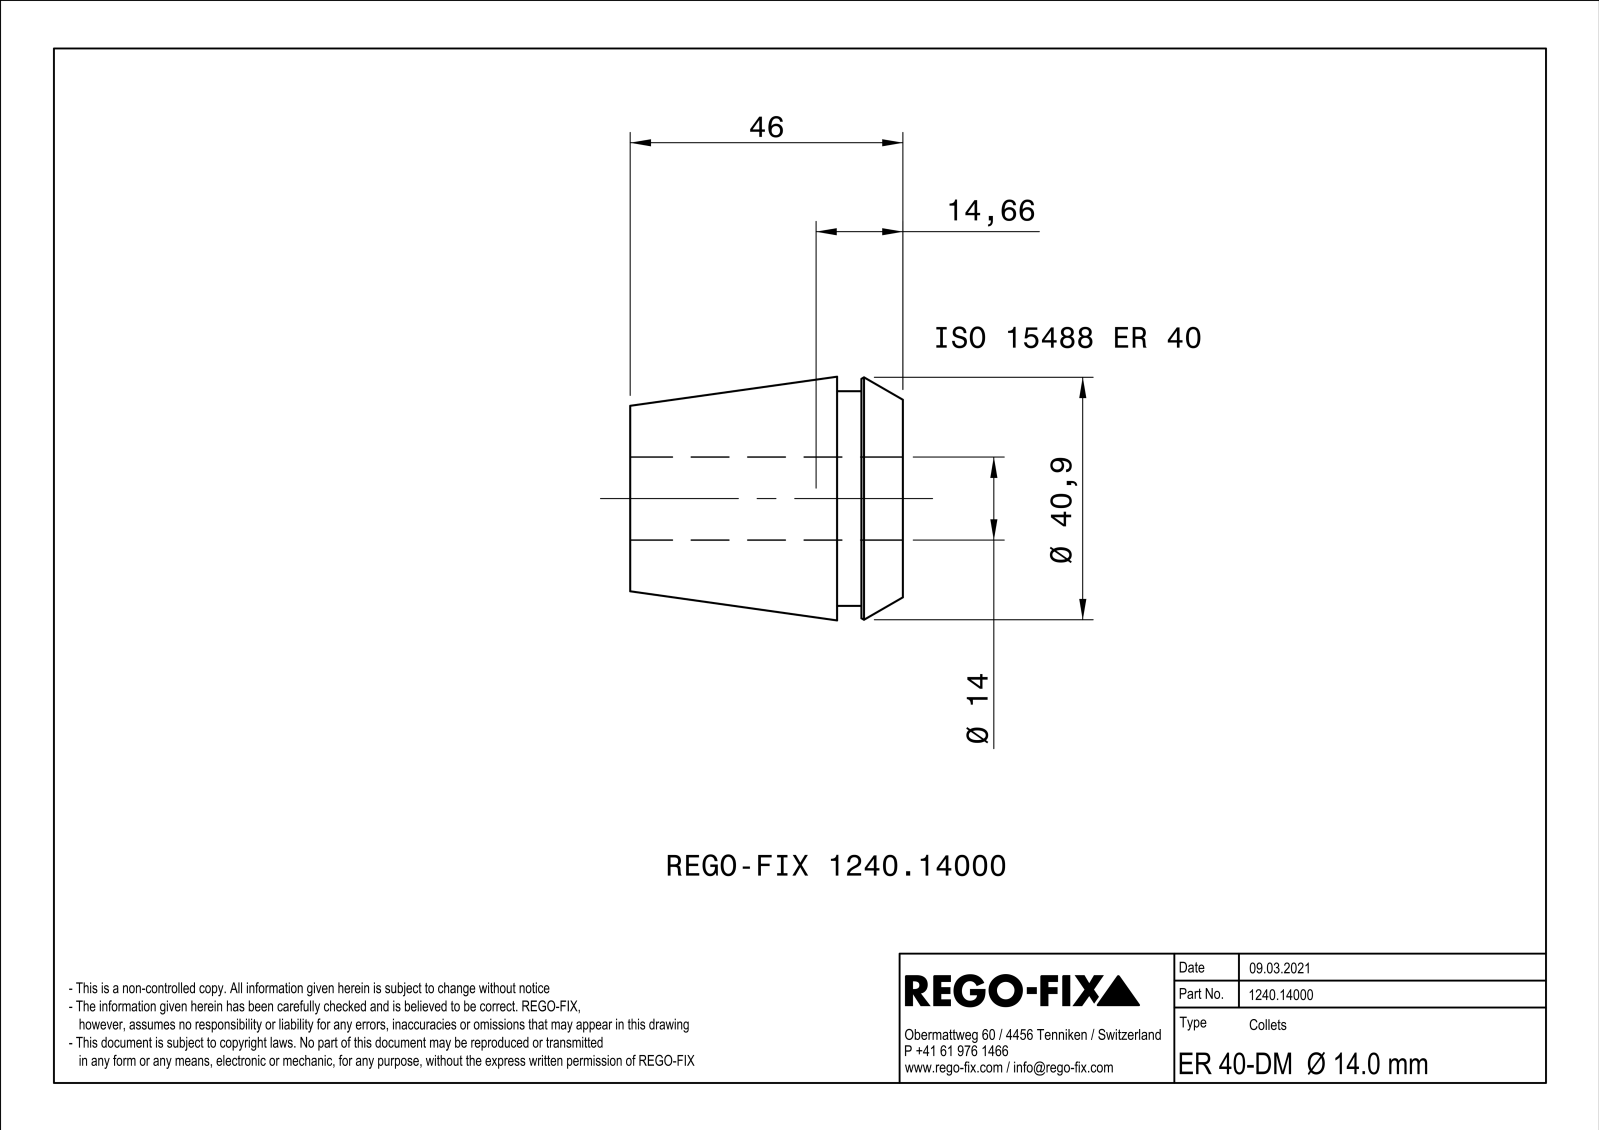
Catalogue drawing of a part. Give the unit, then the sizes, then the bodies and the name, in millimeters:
Units: millimetres
Overall size (bounding box): 46 × 40.99 × 40.99
Round holes (diameter × count): ⌀14 ×1
Round bosses / shafts (diameter × count): ⌀36.2 ×1
Main face-to-face distances: 1, 46, 11.1, 34.9, 7, 4.1, 39, 17, 10, 5.9
Volume: 34 544 mm³ · Surface area: 20 557 mm²
Bodies: 1 solid, 154 faces (80 planar, 9 cylindrical, 65 other)
Part name (STEP PRODUCT): NOCUT
STEP written by: SIEMENS PLM Software Solid Edge ST10 (AUTOMOTIVE_DESIGN)
